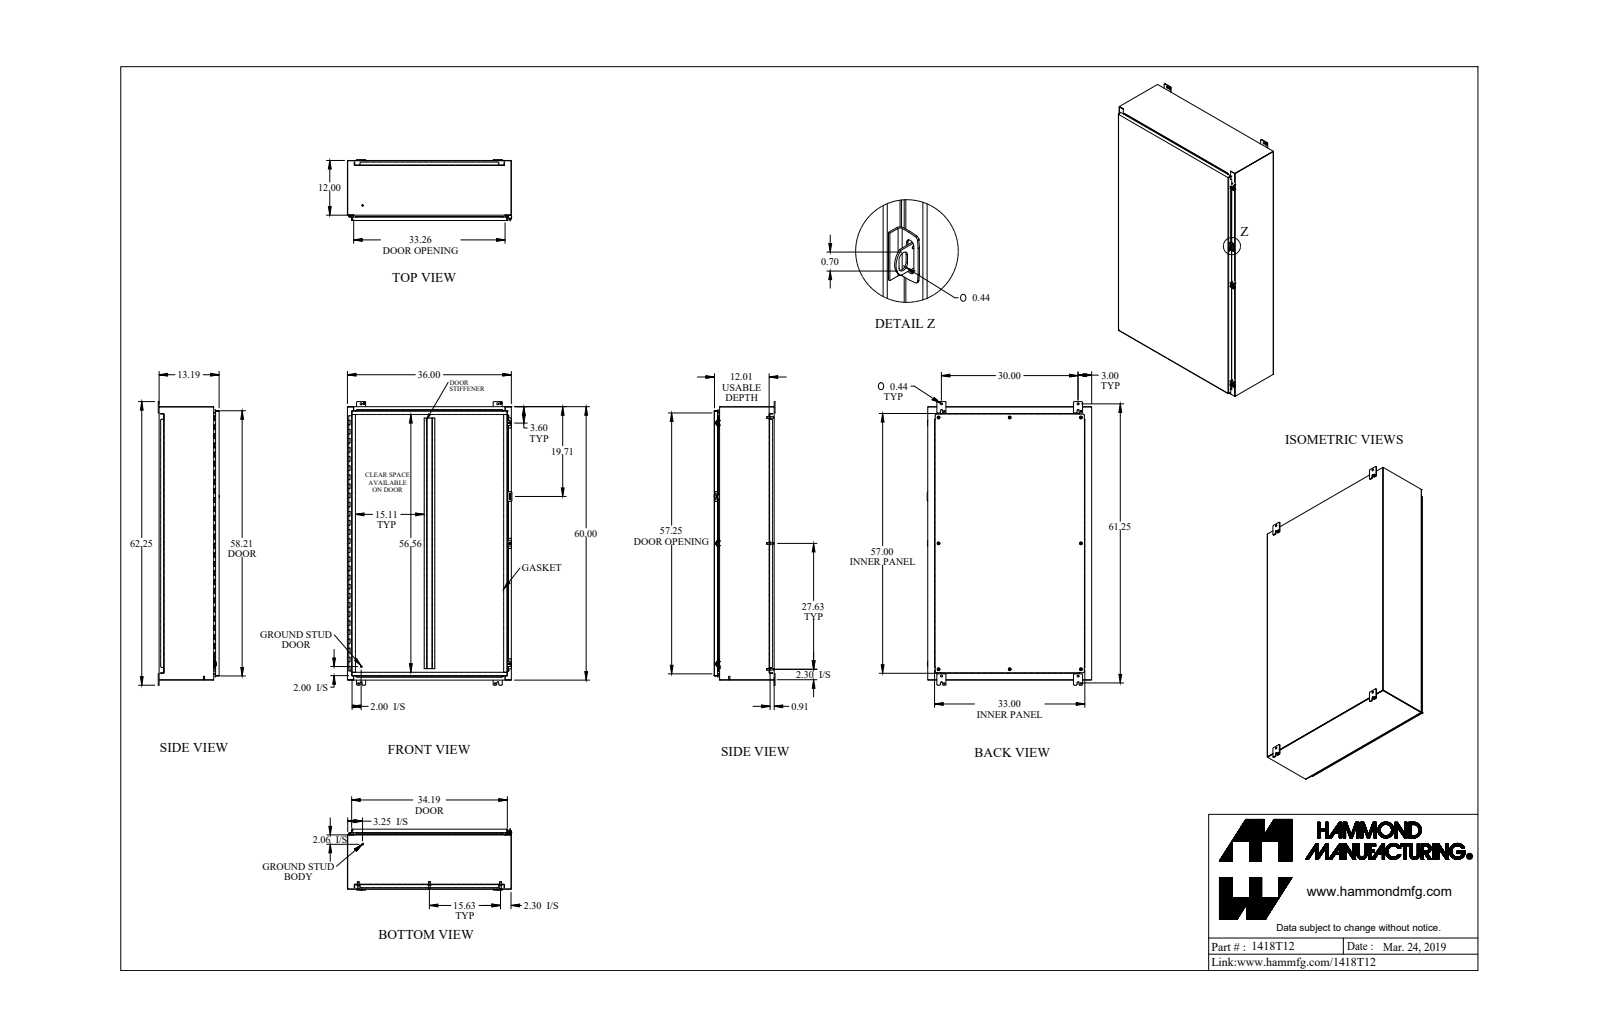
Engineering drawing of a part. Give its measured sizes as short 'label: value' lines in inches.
name: 1418T12_Default
written by: SolidWorks 2019 (CONFIG_CONTROL_DESIGN)
unit: in
bodies: 65 solids, 2055 faces (1202 planar, 730 cylindrical, 123 other)
size: 62.25 × 36.125 × 14.125
volume: 779.5 in³; area: 20 202 in²
holes: 8× ⌀0.5, 5× ⌀0.307, 5× ⌀0.445, 4× ⌀0.313, 4× ⌀0.437, 3× ⌀0.213, 3× ⌀0.265, 3× ⌀0.375, 1× ⌀0.125, 1× ⌀0.187, 1× ⌀0.196, 1× ⌀0.25
bosses: 8× ⌀0.65, 8× ⌀0.375, 8× ⌀0.33, 5× ⌀1, 3× ⌀0.5, 3× ⌀0.39, 3× ⌀0.244, 2× ⌀0.281
rounds: 40× R0.25, 34× R0.188, 22× R0.036, 22× R0.108, 19× R0.048, 19× R0.143, 16× R0.116, 8× R0.125
face distances: 0.072, 13.113, 13.041, 0.937, 13.185, 0.095, 1.009, 12.081, 12.009, 1.032
hole spacings: 31.738, 15.625, 27.625, 57.417, 63.475, 30, 31.25, 41.71
